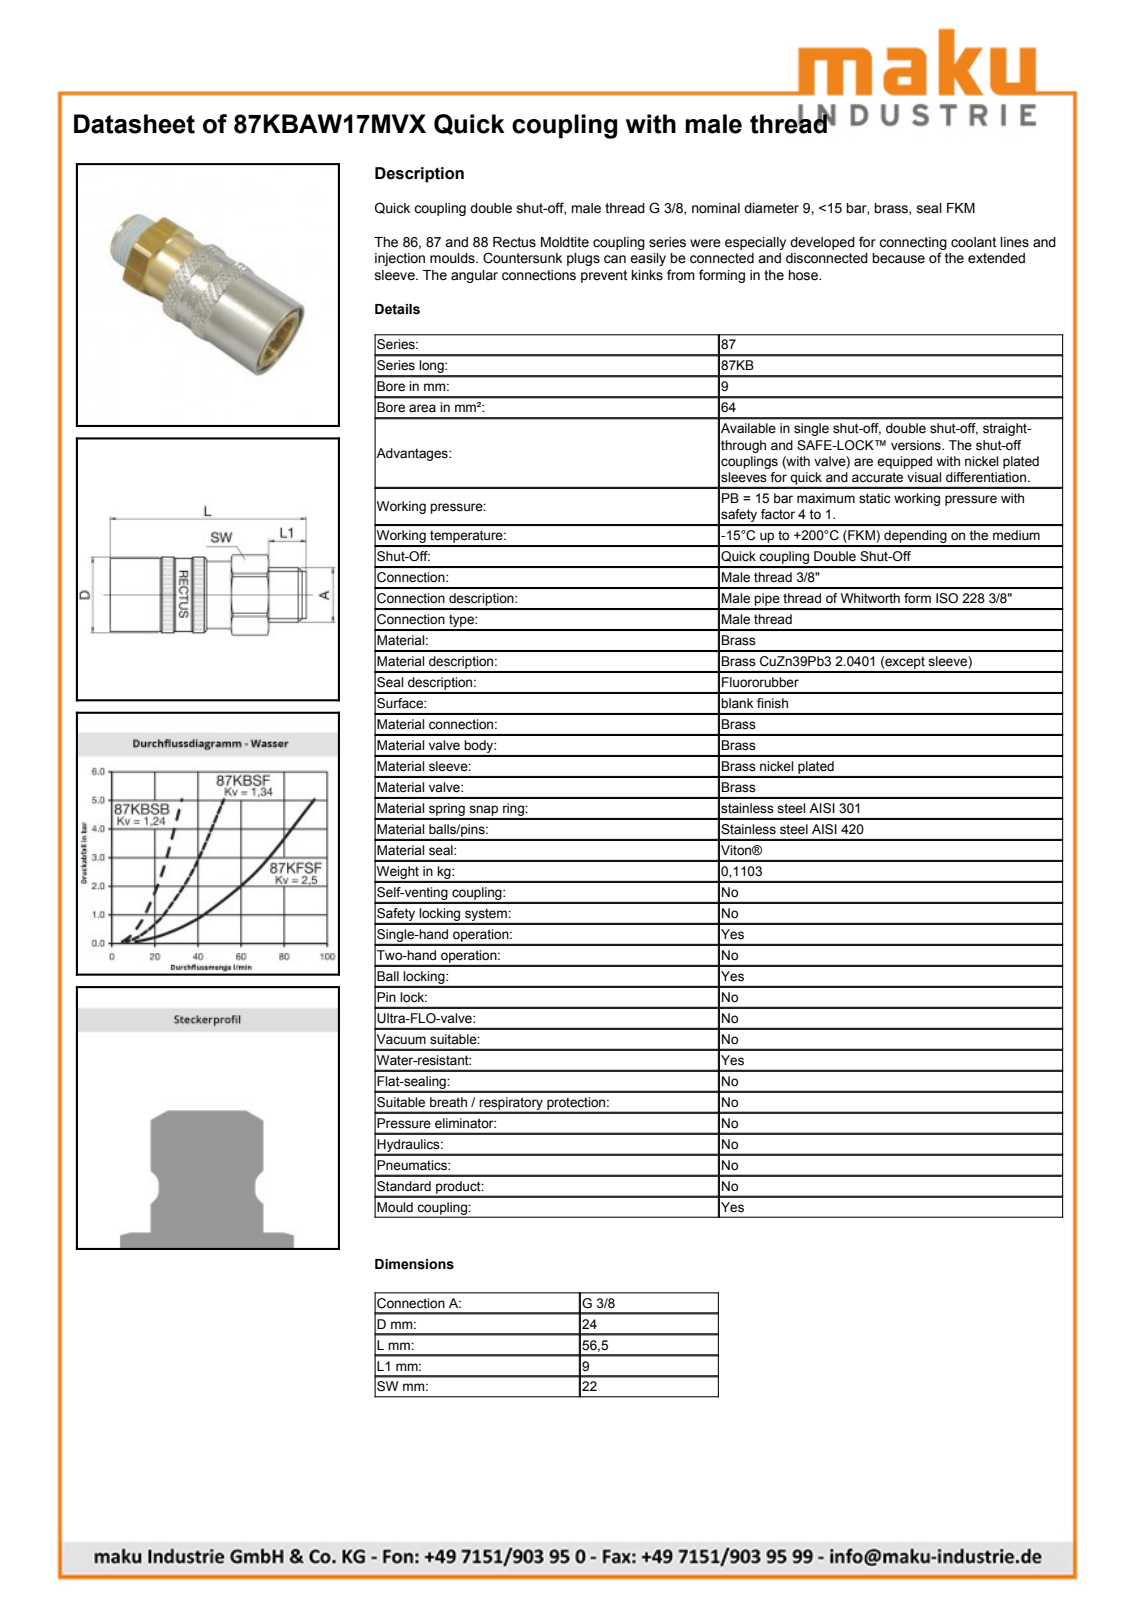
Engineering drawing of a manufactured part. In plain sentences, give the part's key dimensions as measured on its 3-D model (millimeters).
The part is named "D109142". Its 3-D file was written by "Autodesk Inventor 2013 (AUTOMOTIVE_DESIGN)". It is 2 solids with 471 faces: 145 planar, 67 cylindrical and 259 other. Overall it measures 56.6 by 24.8 by 24.15 millimeters. Its volume is 19 584 cubic millimeters and its surface area 10 510 square millimeters. Round holes: 1 of diameter 16, 1 of diameter 17.5, 1 of diameter 18.75, 1 of diameter 21.05, 1 of diameter 21.25. Round bosses or shafts: 1 of diameter 24.15, 1 of diameter 23, 1 of diameter 20.5, 1 of diameter 18, 1 of diameter 17.25, 1 of diameter 16.66, 1 of diameter 16.45, 1 of diameter 15.78. Partial cylindrical surfaces (rounded edges, fillets, slot ends): 1 of radius 11.4, 1 of radius 12.4. The main face-to-face distances are 47.6, 9, 56.6, 22, 45.25, 36.25, 11.35, 22.02, 35, 26.
